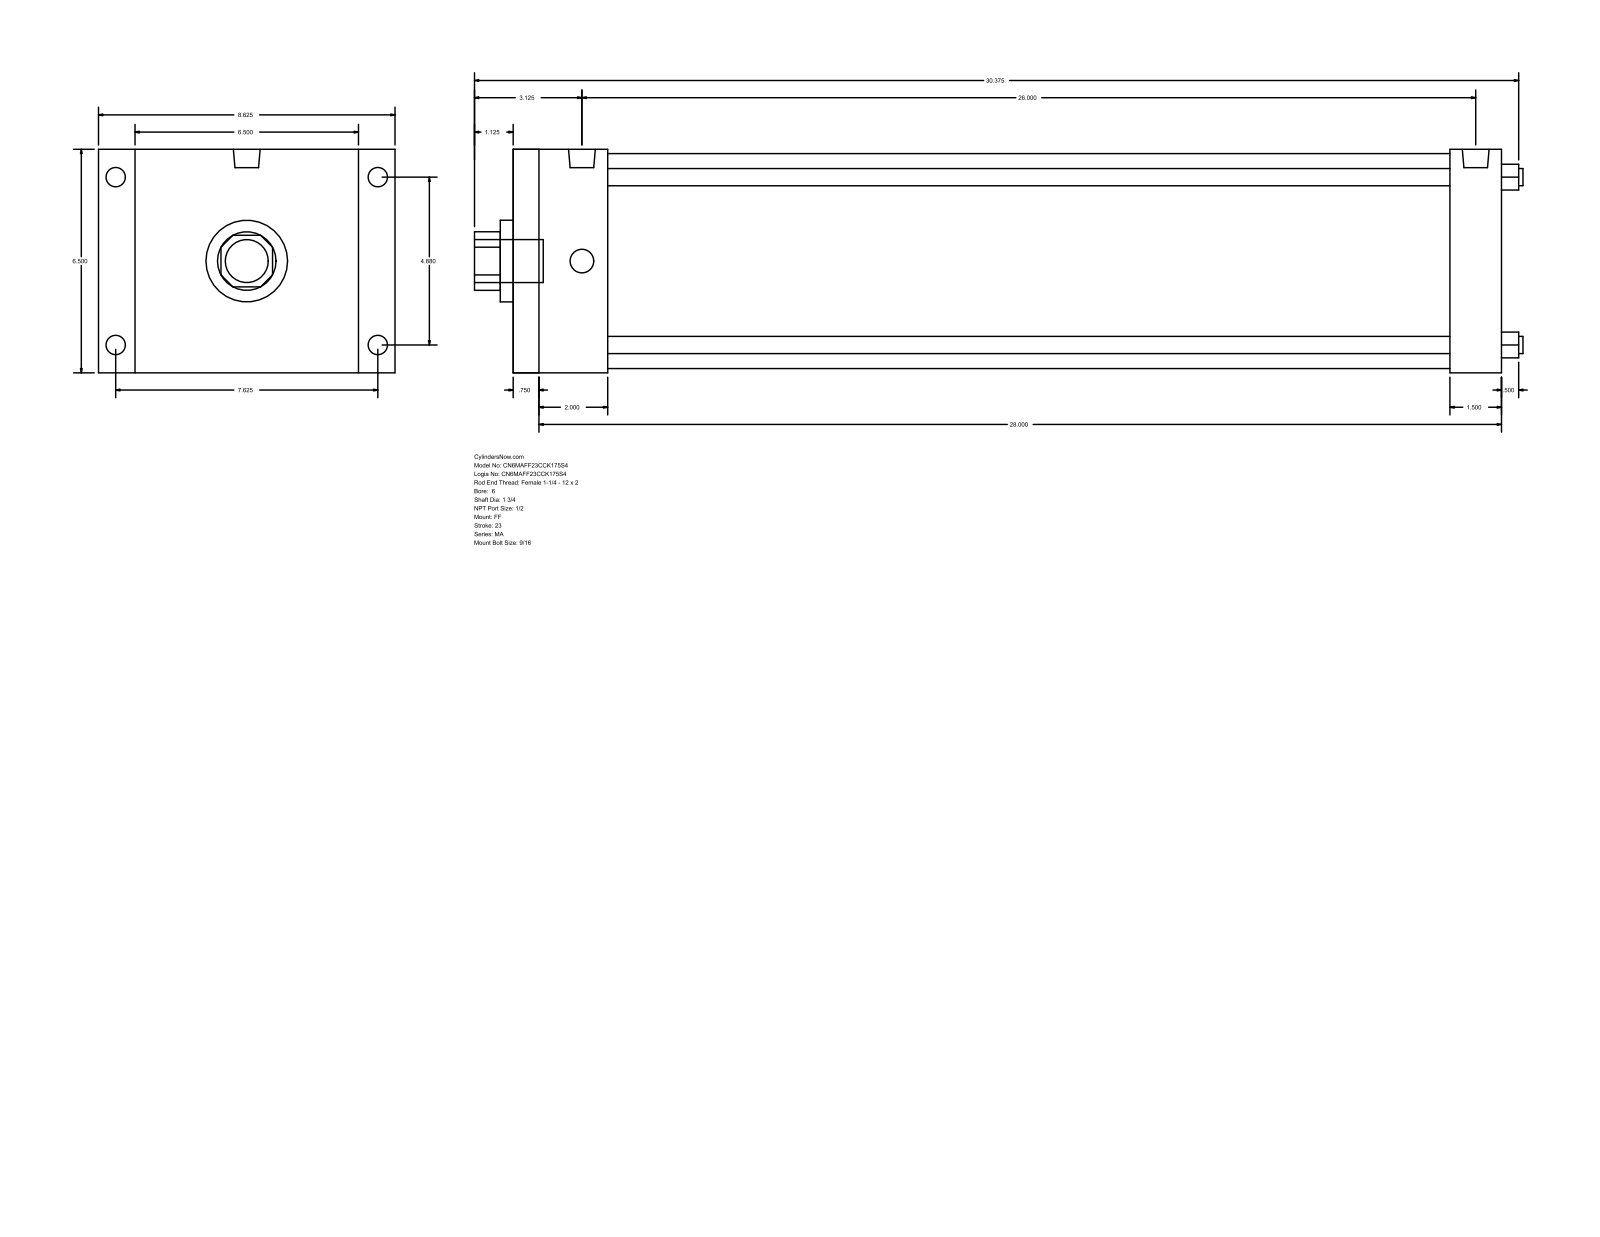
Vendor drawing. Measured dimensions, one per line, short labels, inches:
name: MA_FF__0600_1.75
written by: GSSL Pune (CONFIG_CONTROL_DESIGN)
unit: in
bodies: 0 solids, 92 faces (64 planar, 28 cylindrical, 0 other)
size: 30.5 × 8.625 × 6.5
holes: 4× ⌀0.5, 1× ⌀1.75, 1× ⌀2.375, 1× ⌀6.25
bosses: 4× ⌀0.687, 4× ⌀0.563, 2× ⌀0.778, 1× ⌀1.25
rounds: 1× R0.852
face distances: 6.5, 28.75, 0.75, 28, 1.5, 2, 2.75, 26, 27.25, 26.5
hole spacings: 3.451, 4.88, 6.902
